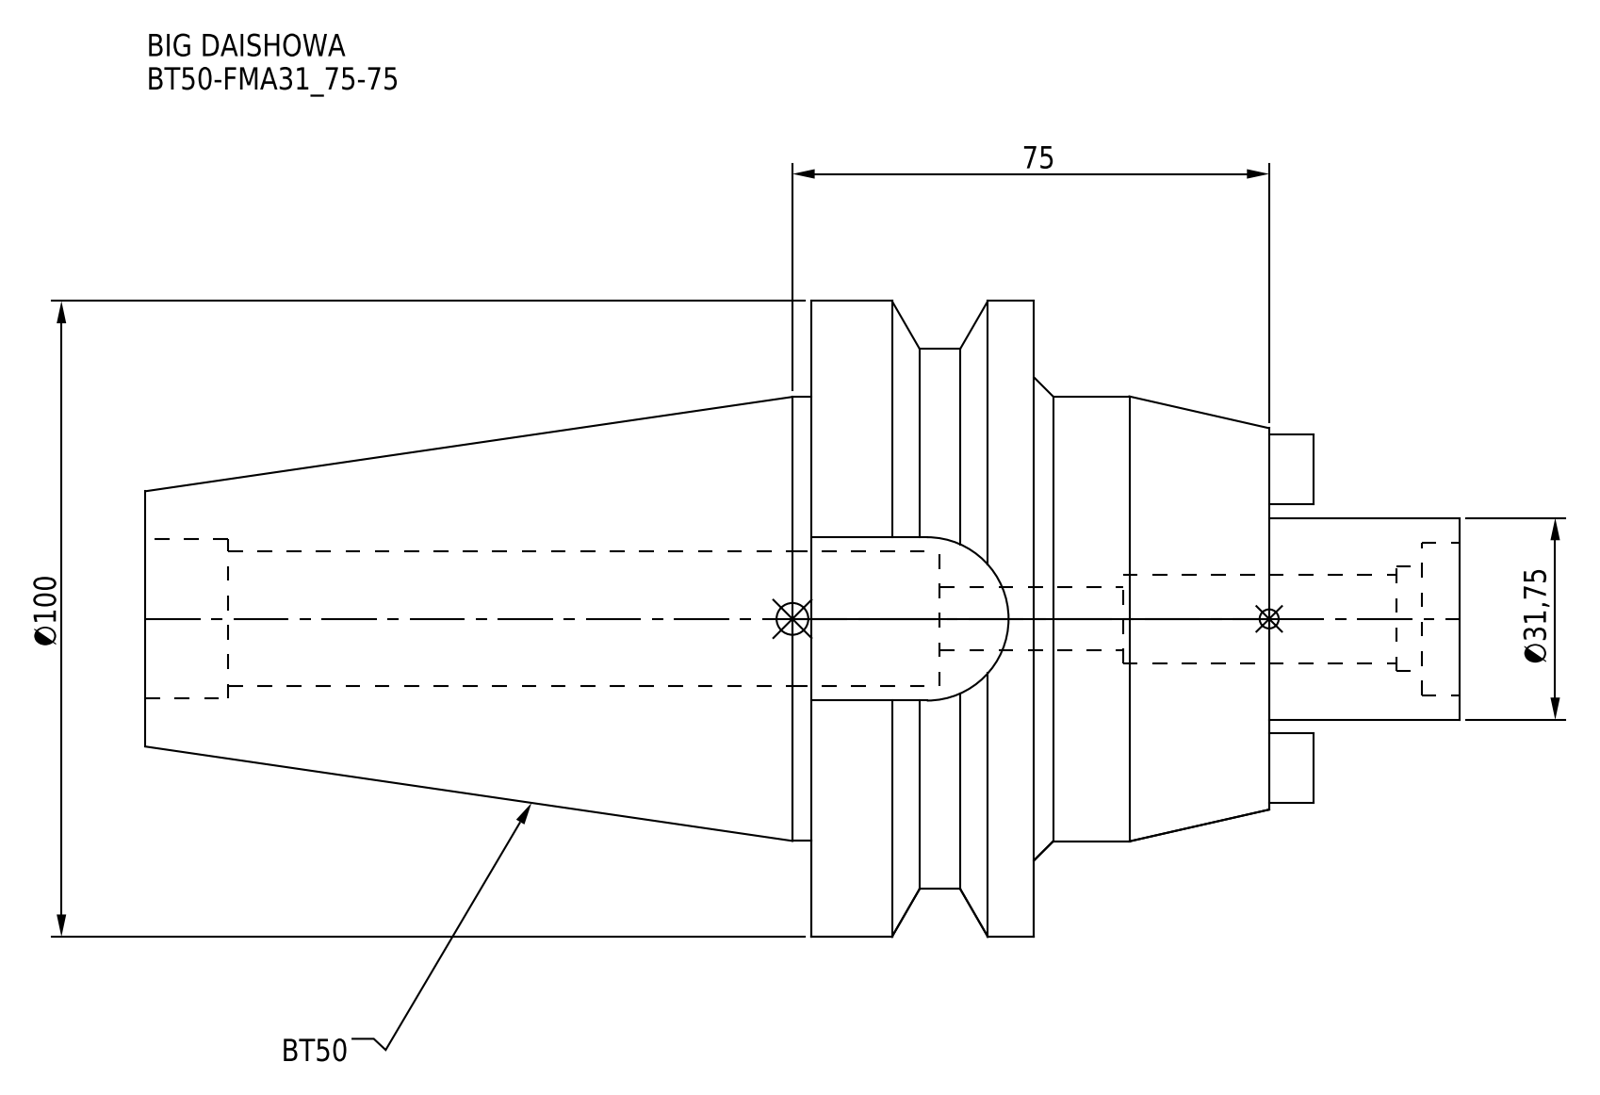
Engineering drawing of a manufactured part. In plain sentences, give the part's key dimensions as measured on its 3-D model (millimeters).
The part is named "BT50-FMA31_75-75". Its 3-D file was written by "CREO PARAMETRIC BY PTC INC, 2016380 (AUTOMOTIVE_DESIGN)". It is 1 solid with 66 faces: 26 planar, 30 cylindrical and 10 other. Overall it measures 206.8 by 100 by 100 millimeters. Its volume is 593 262 cubic millimeters and its surface area 67 081 square millimeters. Round holes: 1 of diameter 10, 1 of diameter 14, 1 of diameter 16.5, 1 of diameter 21.2, 1 of diameter 24, 1 of diameter 25. Round bosses or shafts: 1 of diameter 100, 1 of diameter 85, 1 of diameter 70, 1 of diameter 69.85, 1 of diameter 31.75. Partial cylindrical surfaces (rounded edges, fillets, slot ends): 1 of radius 12.85. The main face-to-face distances are 35, 37, 72, 176.8, 139.8, 104.8, 70.8, 25.7, 30, 23.
